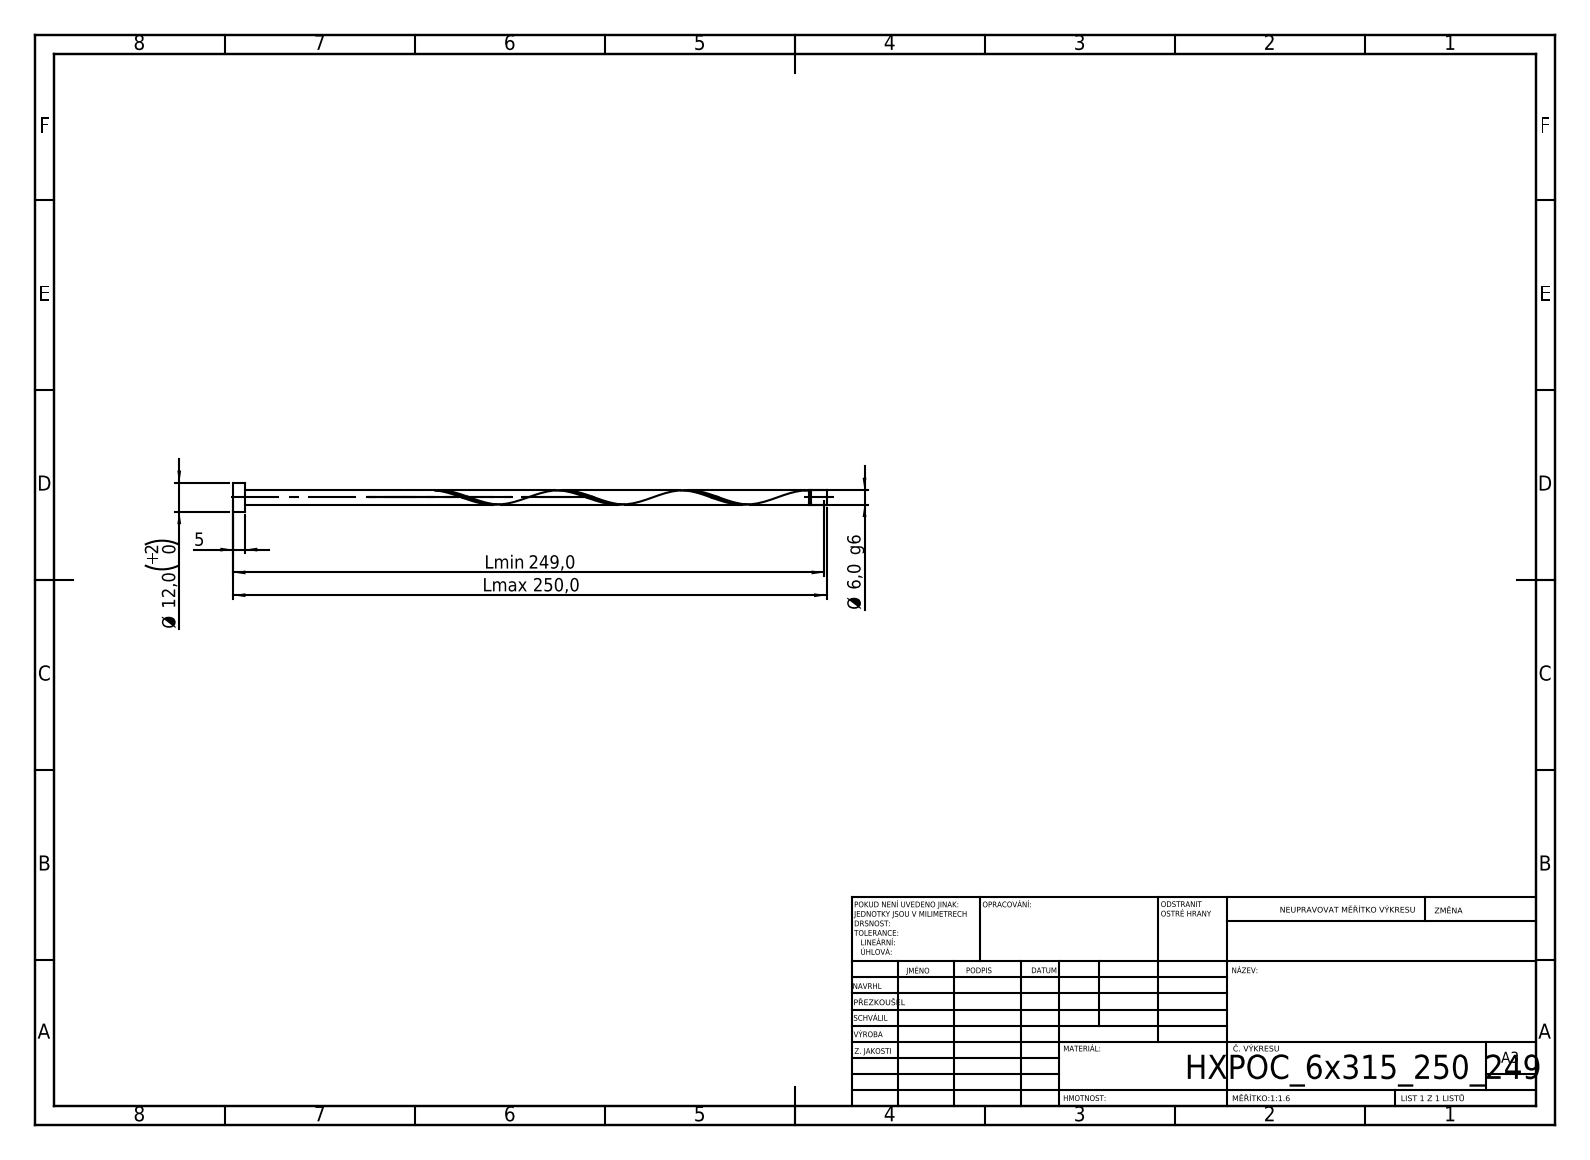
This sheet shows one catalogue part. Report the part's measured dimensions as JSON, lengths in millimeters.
{"step_written_by": "SolidWorks 2019 (CONFIG_CONTROL_DESIGN)", "units": "millimeters", "bodies": {"solids": 1, "faces": 21, "planar": 6, "cylindrical": 14, "other": 1}, "overall_size": [250, 12, 12], "volume_mm3": 7395, "surface_area_mm2": 5145, "round_bosses_or_shafts": [[12, 1], [6, 1], [4.8, 1]], "face_to_face_distances": [5, 250, 245, 243.6, 238.6, 6.4, 242.4, 237.4, 1.2, 7.6]}
